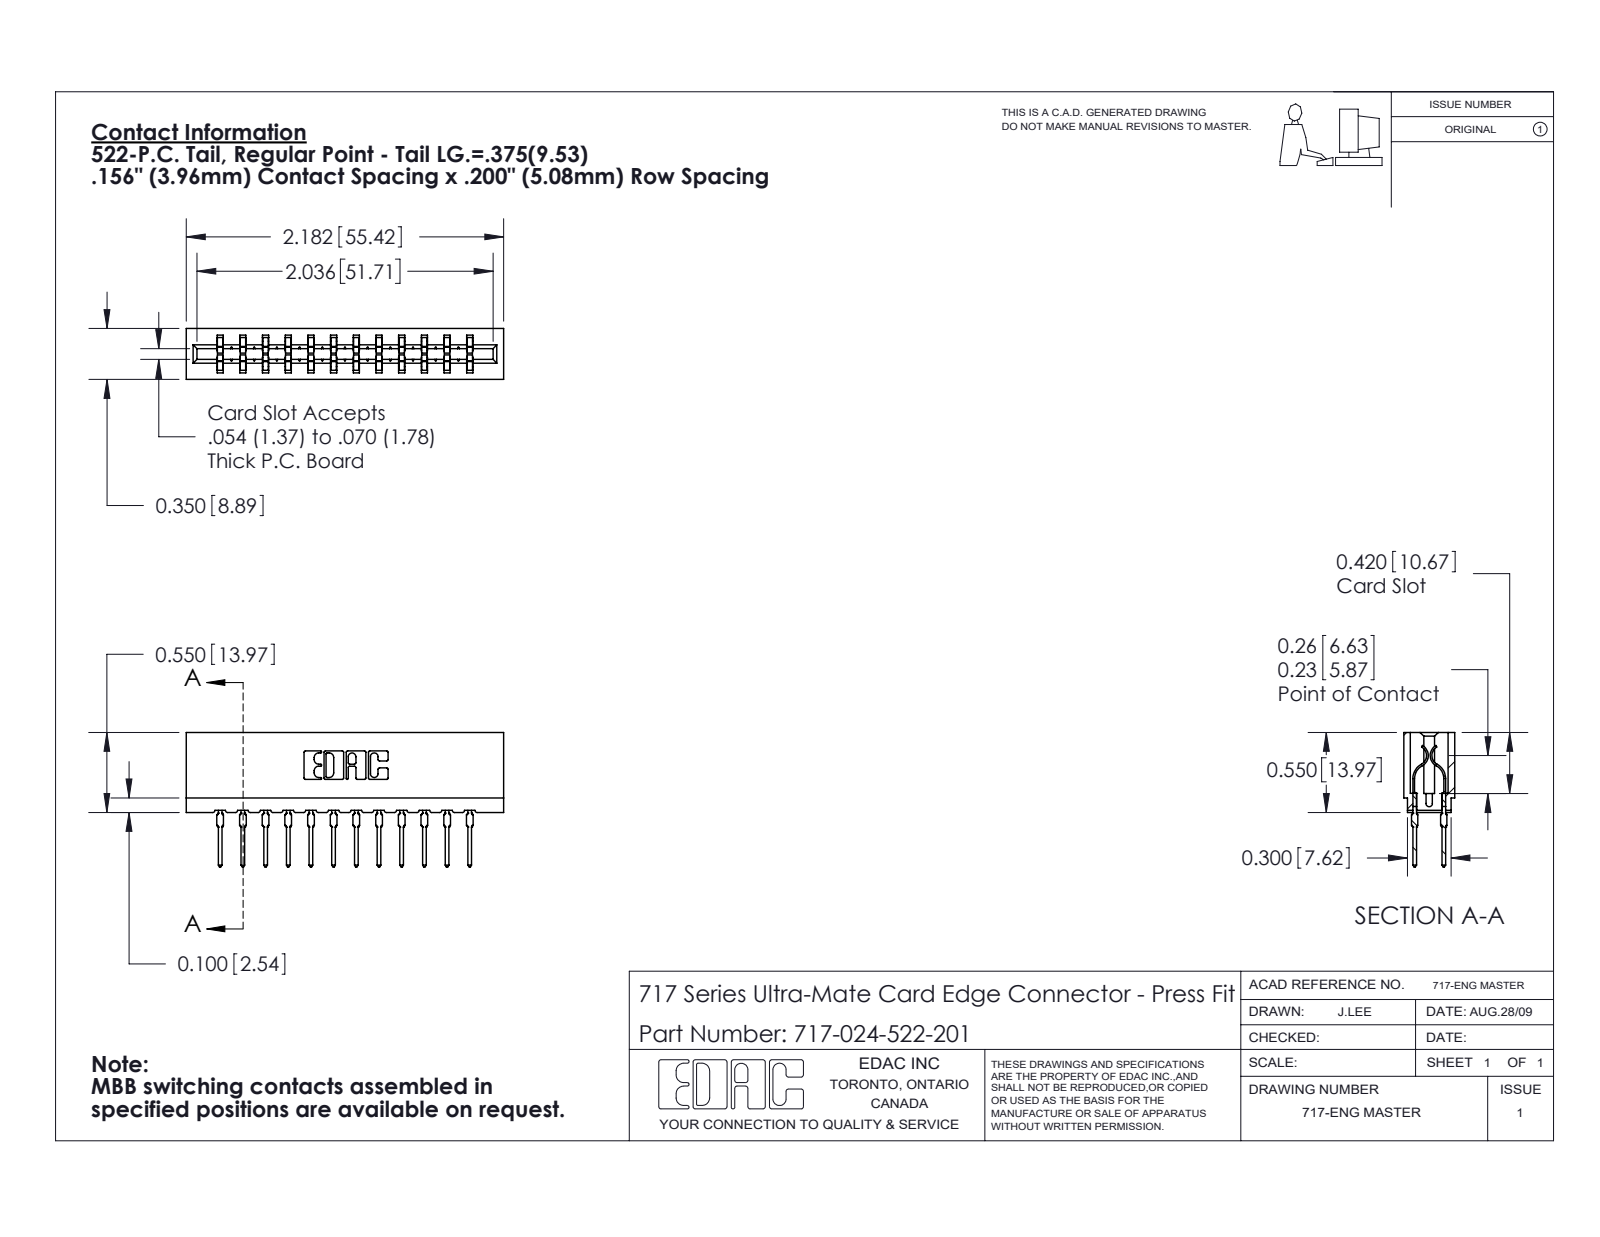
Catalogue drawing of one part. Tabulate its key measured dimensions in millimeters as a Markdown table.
| quantity | value |
| --- | --- |
| part name | 717 Part_Insulator Option - 06; 745-292-001_522; 717-024-522-201 |
| STEP written by | SolidWorks 2020 (CONFIG_CONTROL_DESIGN) |
| units | millimeters |
| bodies | 25 solids, 2254 faces (1170 planar, 460 cylindrical, 624 other) |
| overall size | 55.4 × 23.5 × 8.9 |
| volume | 4 950 mm³ |
| surface area | 7 265 mm² |
| partial cylindrical surfaces (radius × count) | 0.5 × 48, 0.4 × 24, 0.3 × 22, 0.1 × 8, 0.3 × 8, 0.2 × 6, 0.8 × 6, 0.7 × 3 |
| main face-to-face distances | 5.4, 3.5, 4, 15.8, 8.9, 11.9, 5, 7.9, 1.6, 7.3 |
